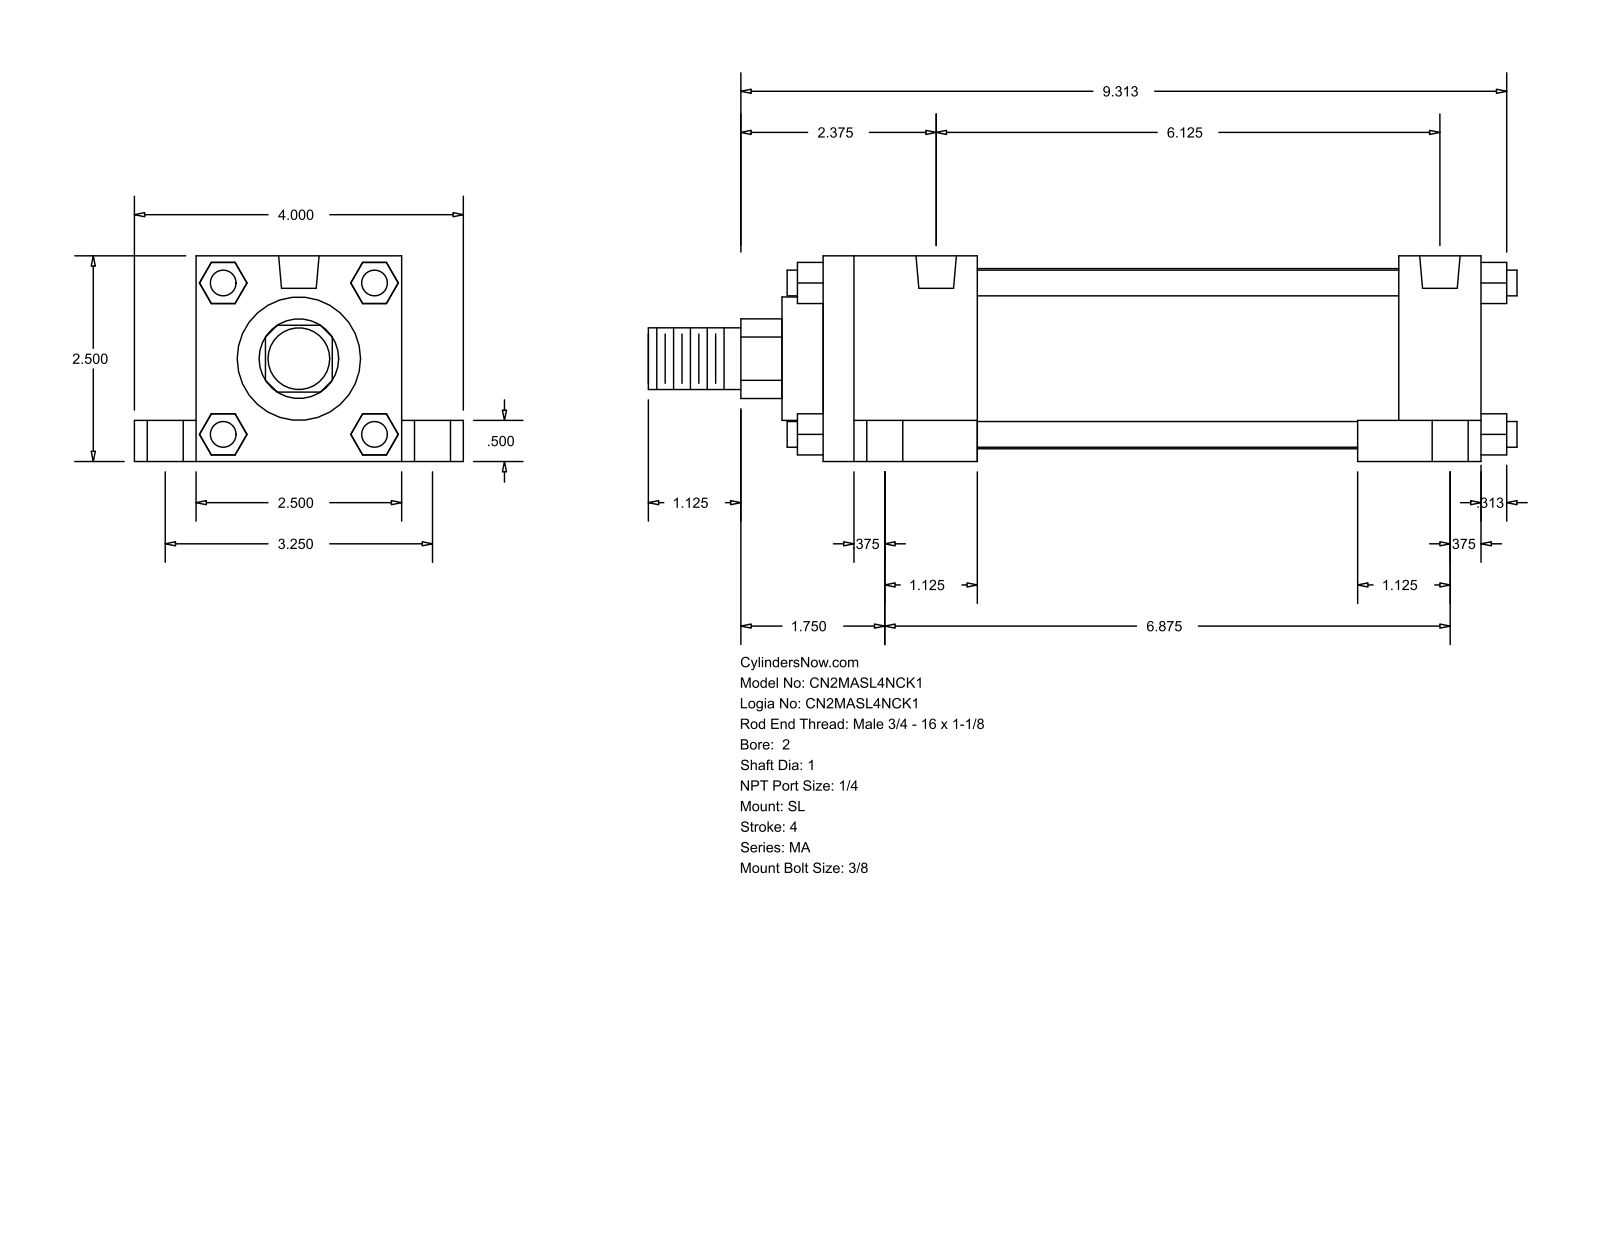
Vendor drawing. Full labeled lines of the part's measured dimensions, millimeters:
Part name (STEP PRODUCT): MA_SL__0200_1
STEP written by: GSSL Pune (CONFIG_CONTROL_DESIGN)
Units: millimetres
Bodies: 0 solids, 148 faces (112 planar, 36 cylindrical, 0 other)
Overall size (bounding box): 268.29 × 101.6 × 63.5
Round holes (diameter × count): ⌀7.94 ×4, ⌀11.11 ×4, ⌀17.46 ×4, ⌀12.49 ×2
Round bosses / shafts (diameter × count): ⌀7.94 ×4, ⌀55.63 ×1, ⌀38.1 ×1, ⌀25.4 ×1, ⌀19.05 ×1
Partial cylindrical surfaces — rounded edges, fillets, slot ends (radius × count): R12.29 ×1
Main face-to-face distances: 63.5, 12.7, 203.2, 19.05, 82.55, 25.4, 50.8, 47.63, 155.57, 177.8
Hole centre spacings: 41.39, 44.22, 82.54, 155.57, 164.02, 174.62, 176.35, 193.15
